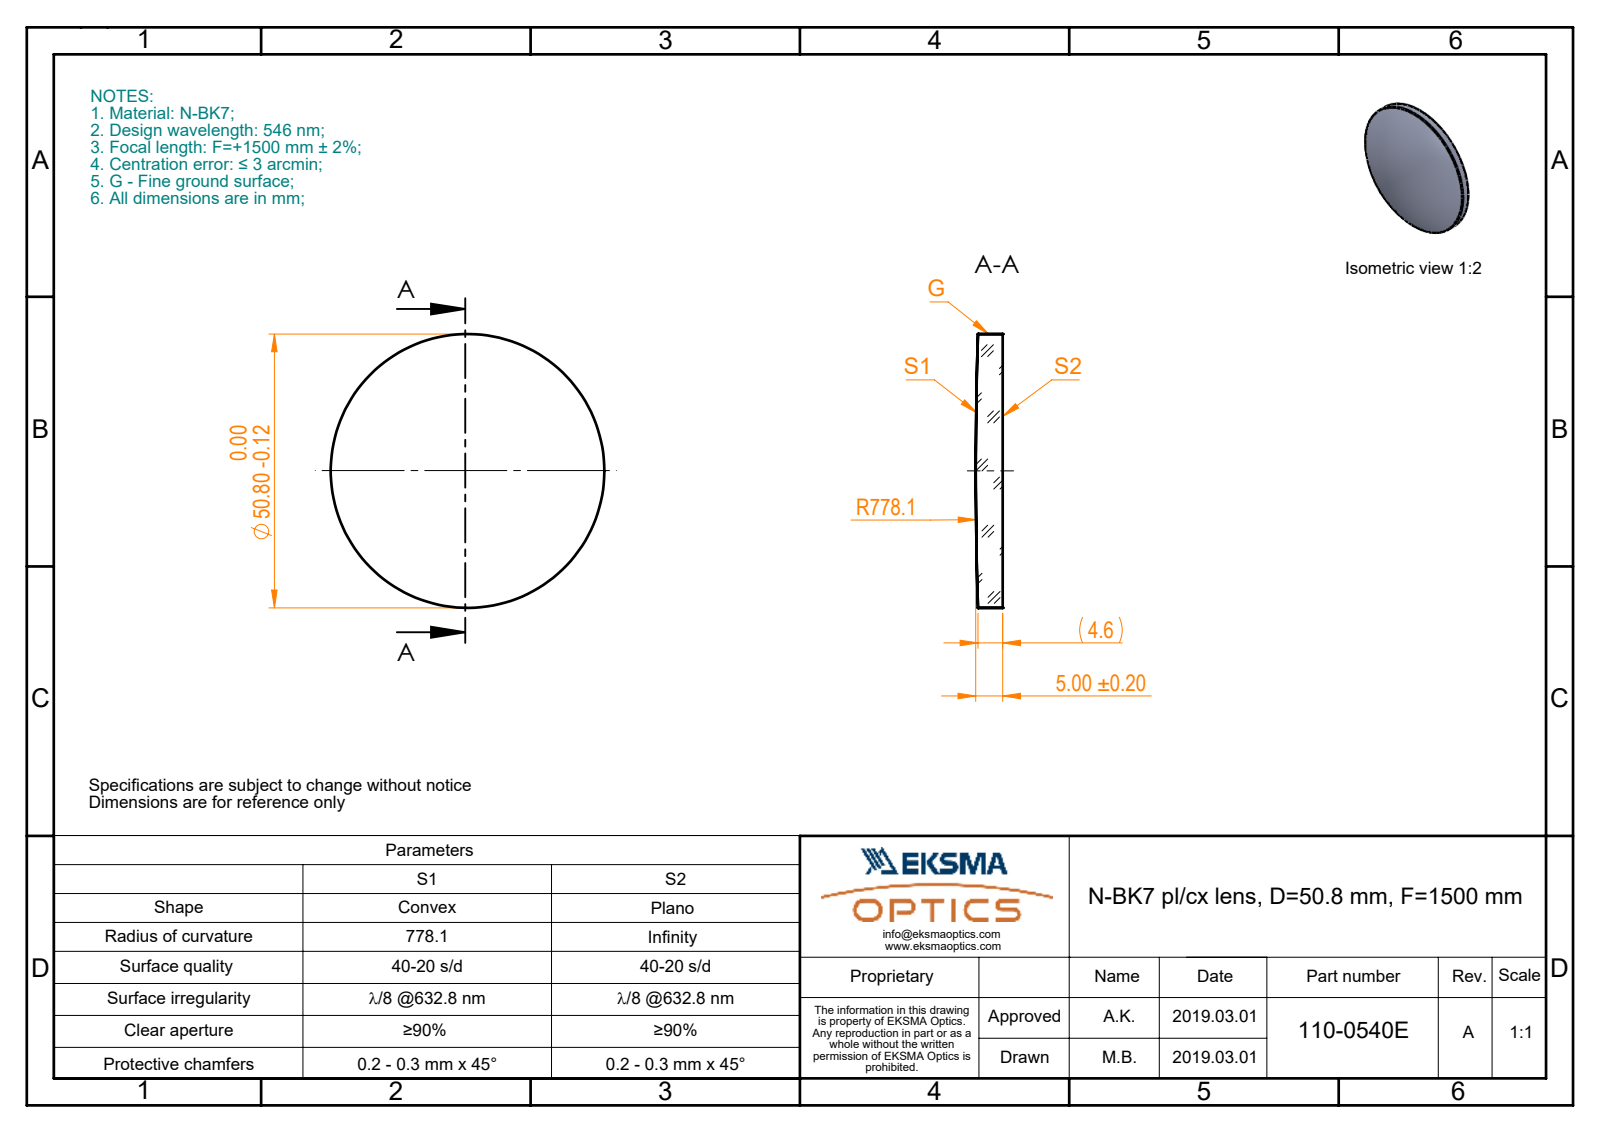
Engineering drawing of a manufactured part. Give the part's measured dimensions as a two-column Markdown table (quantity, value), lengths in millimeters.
| quantity | value |
| --- | --- |
| part name | 110-0540E BK7 pl-cx 50.8 F1500 |
| STEP written by | SolidWorks 2017 (CONFIG_CONTROL_DESIGN) |
| units | millimeters |
| bodies | 1 solid, 5 faces (1 planar, 2 cylindrical, 2 other) |
| overall size | 50.8 × 50.8 × 5 |
| volume | 9 714 mm³ |
| surface area | 4 786 mm² |
| round bosses / shafts (diameter × count) | 50.8 × 1 |
